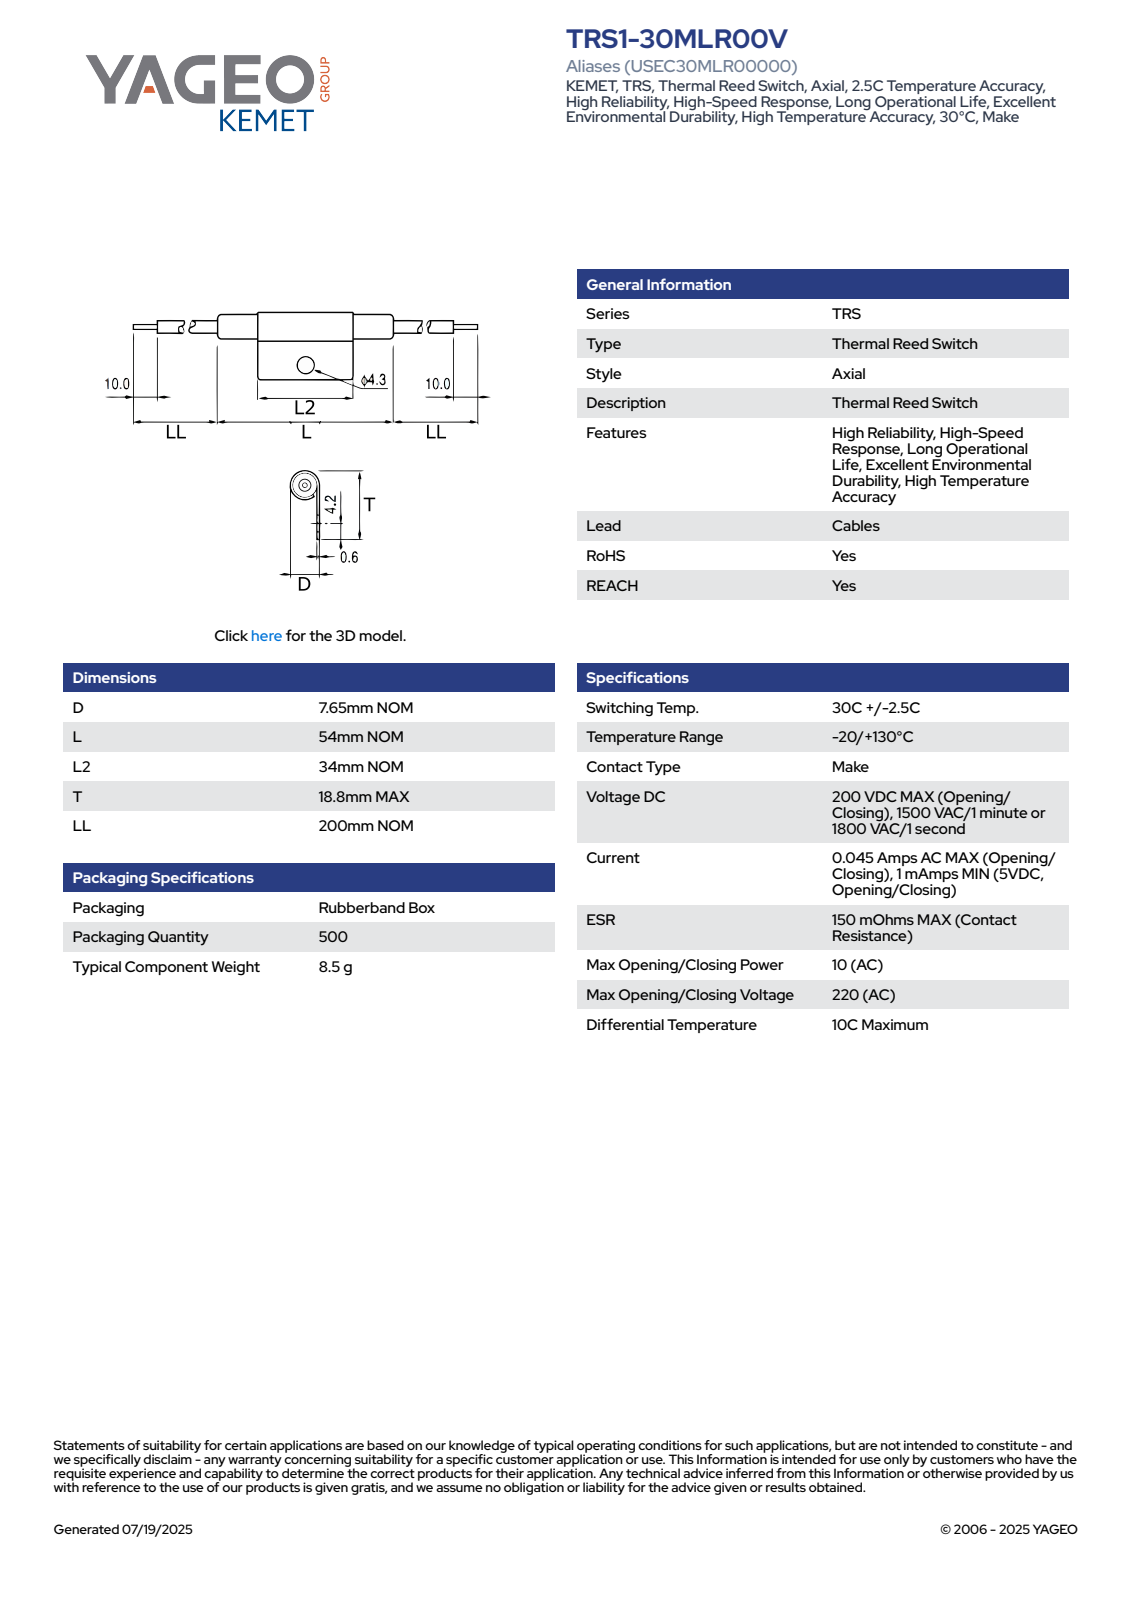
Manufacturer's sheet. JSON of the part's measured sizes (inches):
{"part_name": "ST_TRSL_D7.65L54L234T18.8LL200", "step_written_by": "SolidWorks 2014 (AUTOMOTIVE_DESIGN)", "units": "inches", "bodies": {"solids": 1, "faces": 90, "planar": 33, "cylindrical": 22, "other": 35}, "overall_size": [17.874, 0.74, 0.301], "volume_in3": 0.183, "surface_area_in2": 5.375, "round_holes": [[0.169, 1]], "round_bosses_or_shafts": [[0.301, 1], [0.293, 1], [0.039, 1], [0.02, 1]], "partial_cylinders_radius": [[0.079, 2], [0.15, 1]], "face_to_face_distances": [0.024, 2.126, 0.394, 1.732, 1.339, 7.874, 9.606, 7.48, 9.213, 17.087]}
